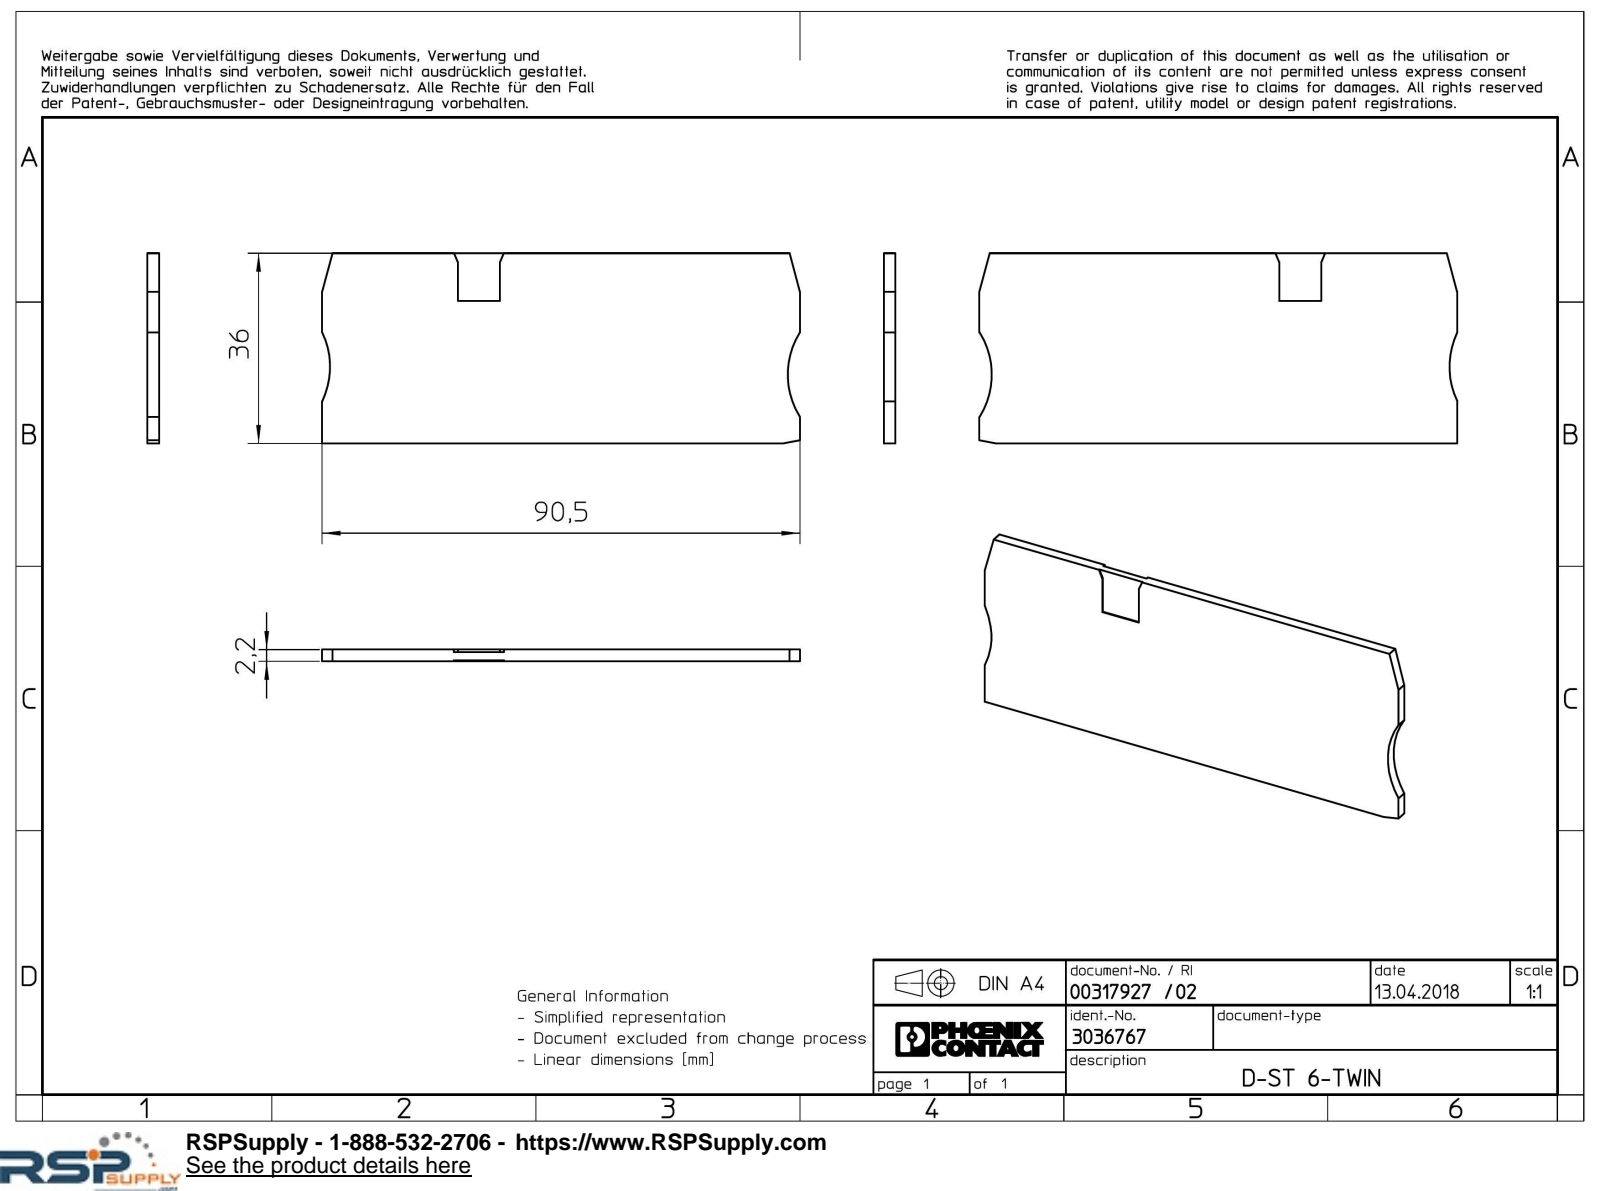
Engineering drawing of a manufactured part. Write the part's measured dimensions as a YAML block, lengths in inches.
part_name: "D_ST_6_TWIN-select"
step_written_by: "Creo Elements/Direct Modeling 18.1I 14-Aug-2016 (C) Parametric Technology GmbH (AUTOMOTIVE_DESIGN)"
units: inches
bodies: {solids: 1, faces: 25, planar: 23, cylindrical: 2, other: 0}
overall_size: [3.563, 1.417, 0.087]
volume: 0.427
surface_area: 10.81
partial_cylinders:
  - {radius: 0.591, count: 2}
face_to_face_distances: [0.087, 1.417, 0.02, 0.079, 0.059, 0.067, 3.563, 1.063, 0.354, 1.327]
